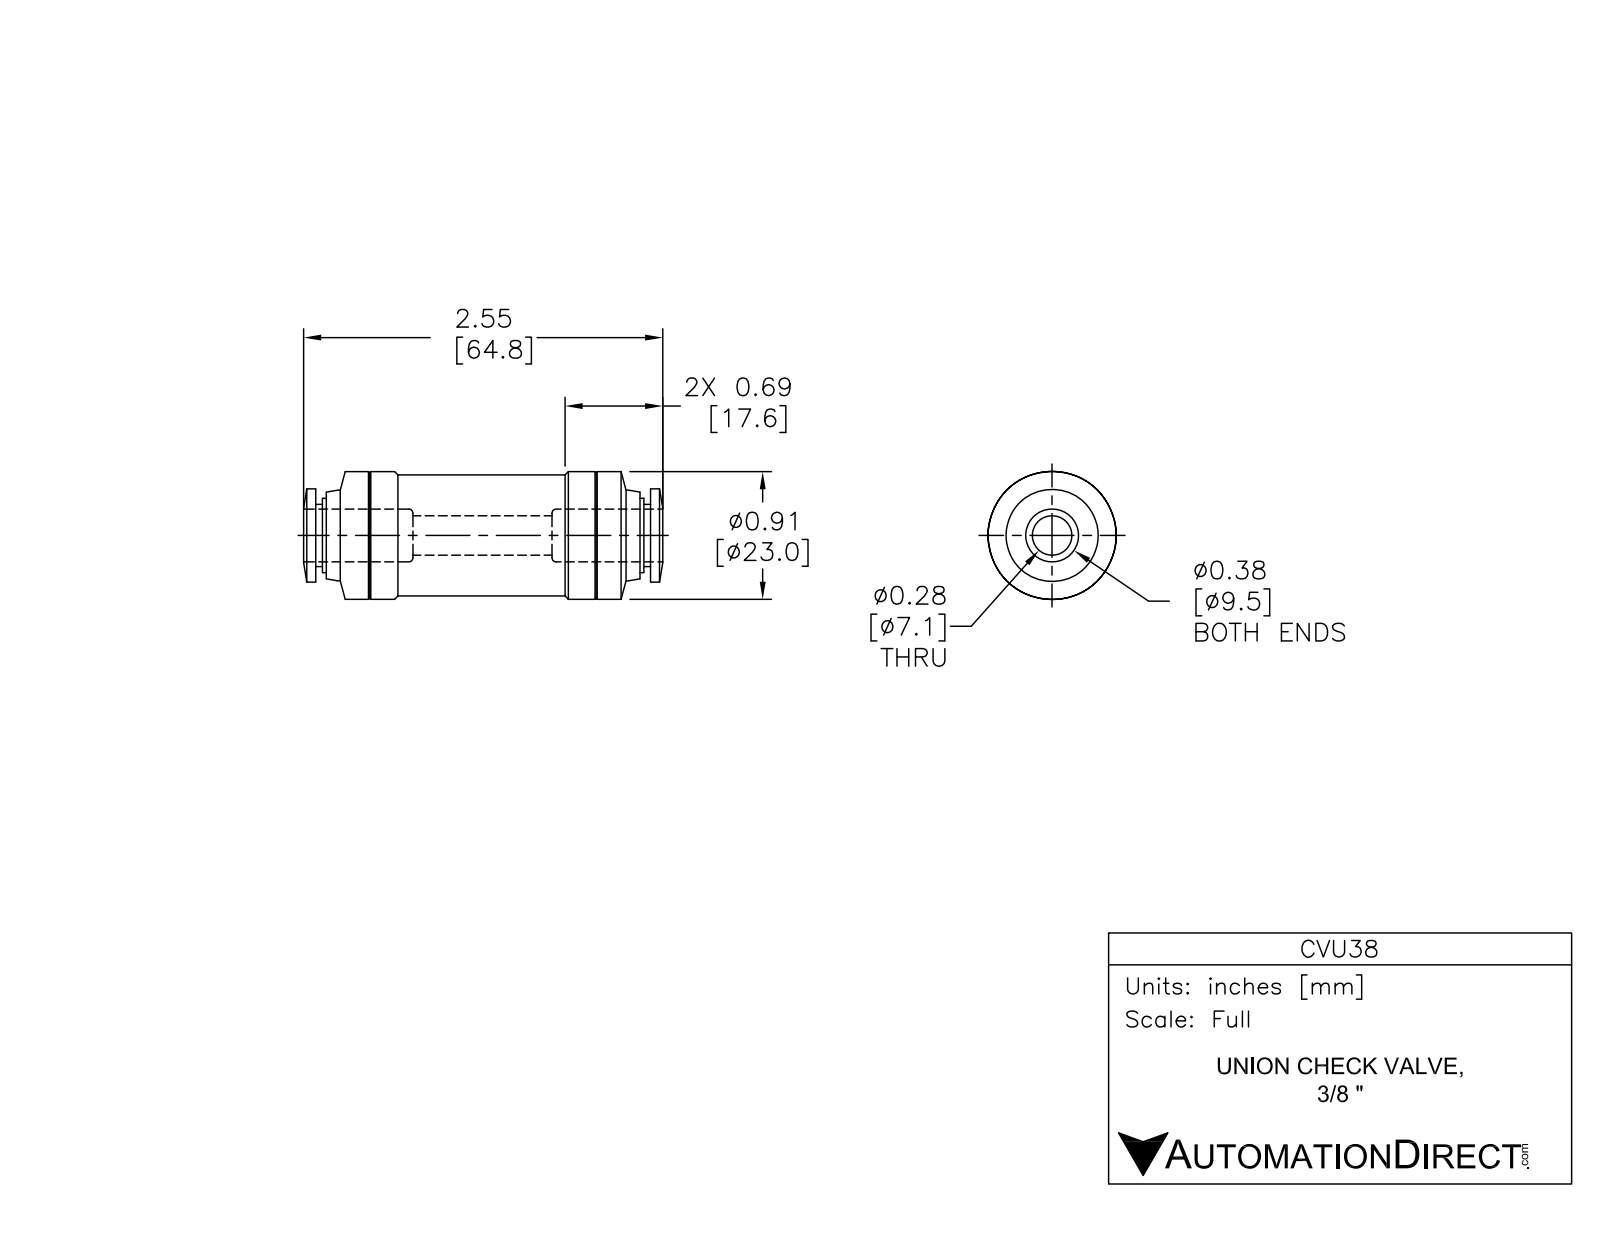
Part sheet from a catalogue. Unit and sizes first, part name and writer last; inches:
Units: inches
Overall size (bounding box): 2.547 × 0.906 × 0.906
Round holes (diameter × count): ⌀0.343 ×1, ⌀0.386 ×1
Round bosses / shafts (diameter × count): ⌀0.906 ×1, ⌀0.858 ×1, ⌀0.661 ×1, ⌀0.642 ×1, ⌀0.528 ×1, ⌀0.441 ×1
Main face-to-face distances: 2.374, 0.075, 2.299, 0.047, 2.327, 0.028, 2.252, 2.224, 2.28, 0.705
Volume: 1.083 in³ · Surface area: 11.15 in²
Bodies: 1 solid, 79 faces (9 planar, 32 cylindrical, 38 other)
Part name (STEP PRODUCT): CVU38
STEP written by: SolidWorks 2015 (AUTOMOTIVE_DESIGN)
